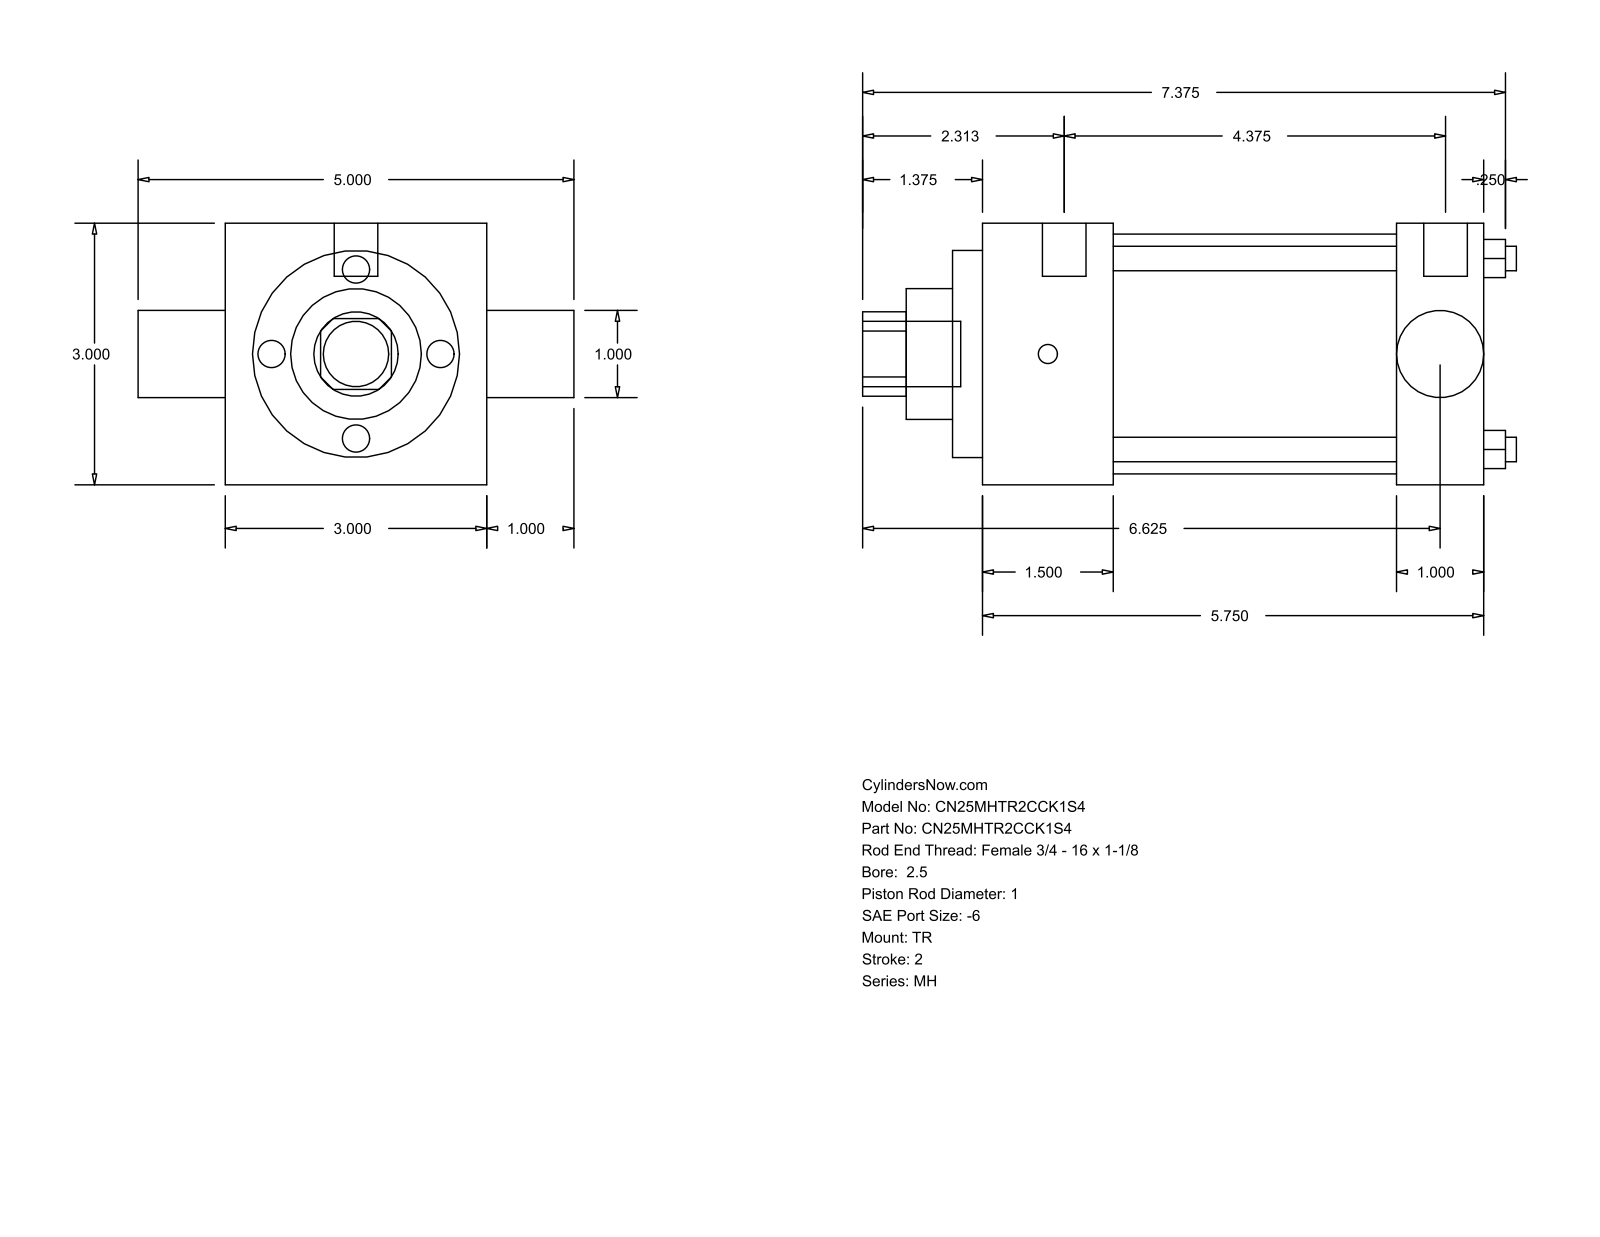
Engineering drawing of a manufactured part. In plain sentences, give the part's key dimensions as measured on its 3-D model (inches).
The part is named "MH_TR__0250_1". Its 3-D file was written by "GSSL Pune (CONFIG_CONTROL_DESIGN)". It is 0 solids with 86 faces: 61 planar, 25 cylindrical and 0 other. Overall it measures 7.5 by 5 by 3 inches. Round holes: 4 of diameter 0.281, 1 of diameter 0.998, 1 of diameter 1, 1 of diameter 1.5, 1 of diameter 2.375, 1 of diameter 2.75. Round bosses or shafts: 3 of diameter 0.219, 2 of diameter 0.5, 1 of diameter 0.75. Partial cylindrical surfaces (rounded edges, fillets, slot ends): 1 of radius 0.484. The main face-to-face distances are 3, 5.75, 1, 1.5, 4.25, 4.75, 3.25, 0.344, 1.844, 5.094. The hole center spacings are 1.548, 2.19, 3.097.
